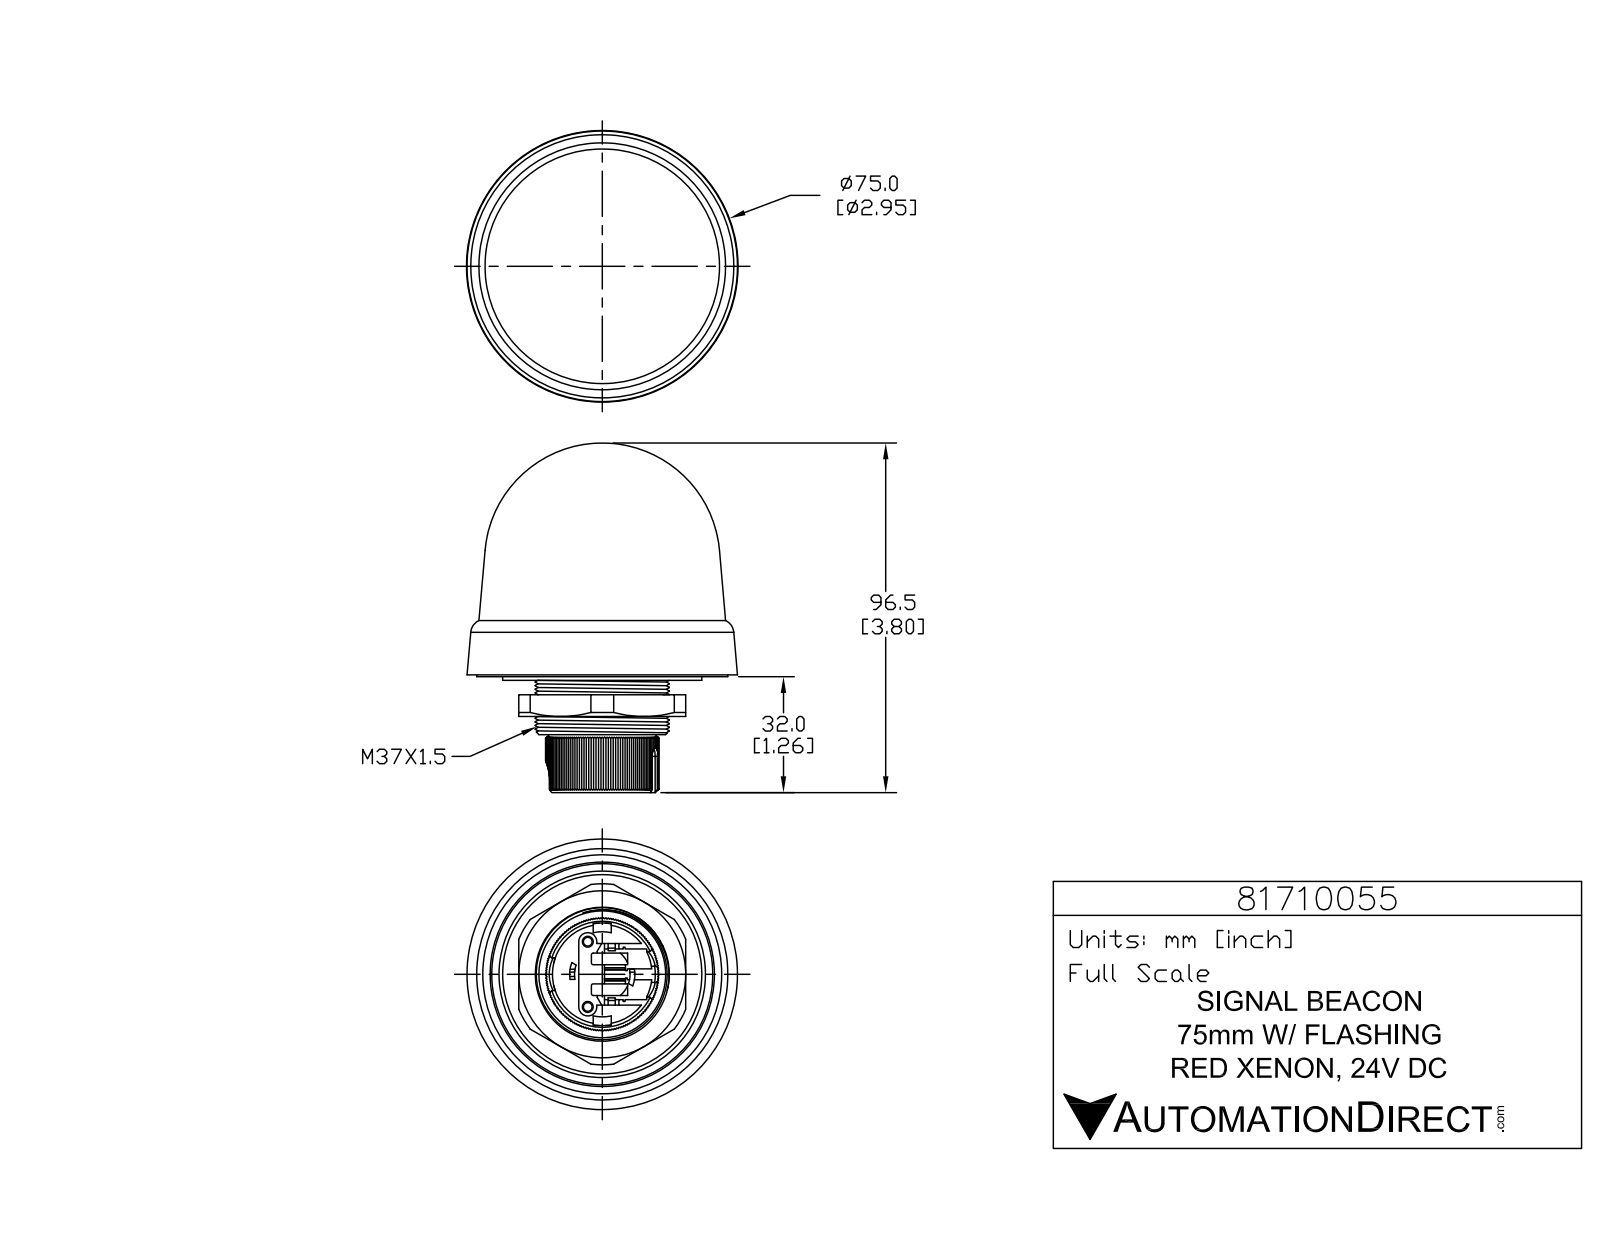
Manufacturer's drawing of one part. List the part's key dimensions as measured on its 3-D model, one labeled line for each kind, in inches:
Part name (STEP PRODUCT): 81710055
STEP written by: SolidWorks 2019 (CONFIG_CONTROL_DESIGN)
Units: inches
Bodies: 3 solids, 560 faces (432 planar, 80 cylindrical, 48 other)
Overall size (bounding box): 3.799 × 2.941 × 2.941
Volume: 12.36 in³ · Surface area: 58.68 in²
Round holes (diameter × count): ⌀0.094 ×2, ⌀0.118 ×2, ⌀0.604 ×1, ⌀1.142 ×1
Round bosses / shafts (diameter × count): ⌀0.217 ×2, ⌀0.067 ×2, ⌀2.165 ×1, ⌀1.457 ×1, ⌀0.925 ×1
Partial cylindrical surfaces — rounded edges, fillets, slot ends (radius × count): R0.008 ×6, R0.039 ×6, R0.02 ×4, R0.031 ×2, R0.079 ×2, R0.098 ×2, R0.177 ×1, R0.354 ×1
Main face-to-face distances: 0.177, 0.354, 0.197, 0.433, 0.512, 0.335, 0.059, 0.394, 0.118, 0.157
Hole centre spacings: 0.388, 0.709
